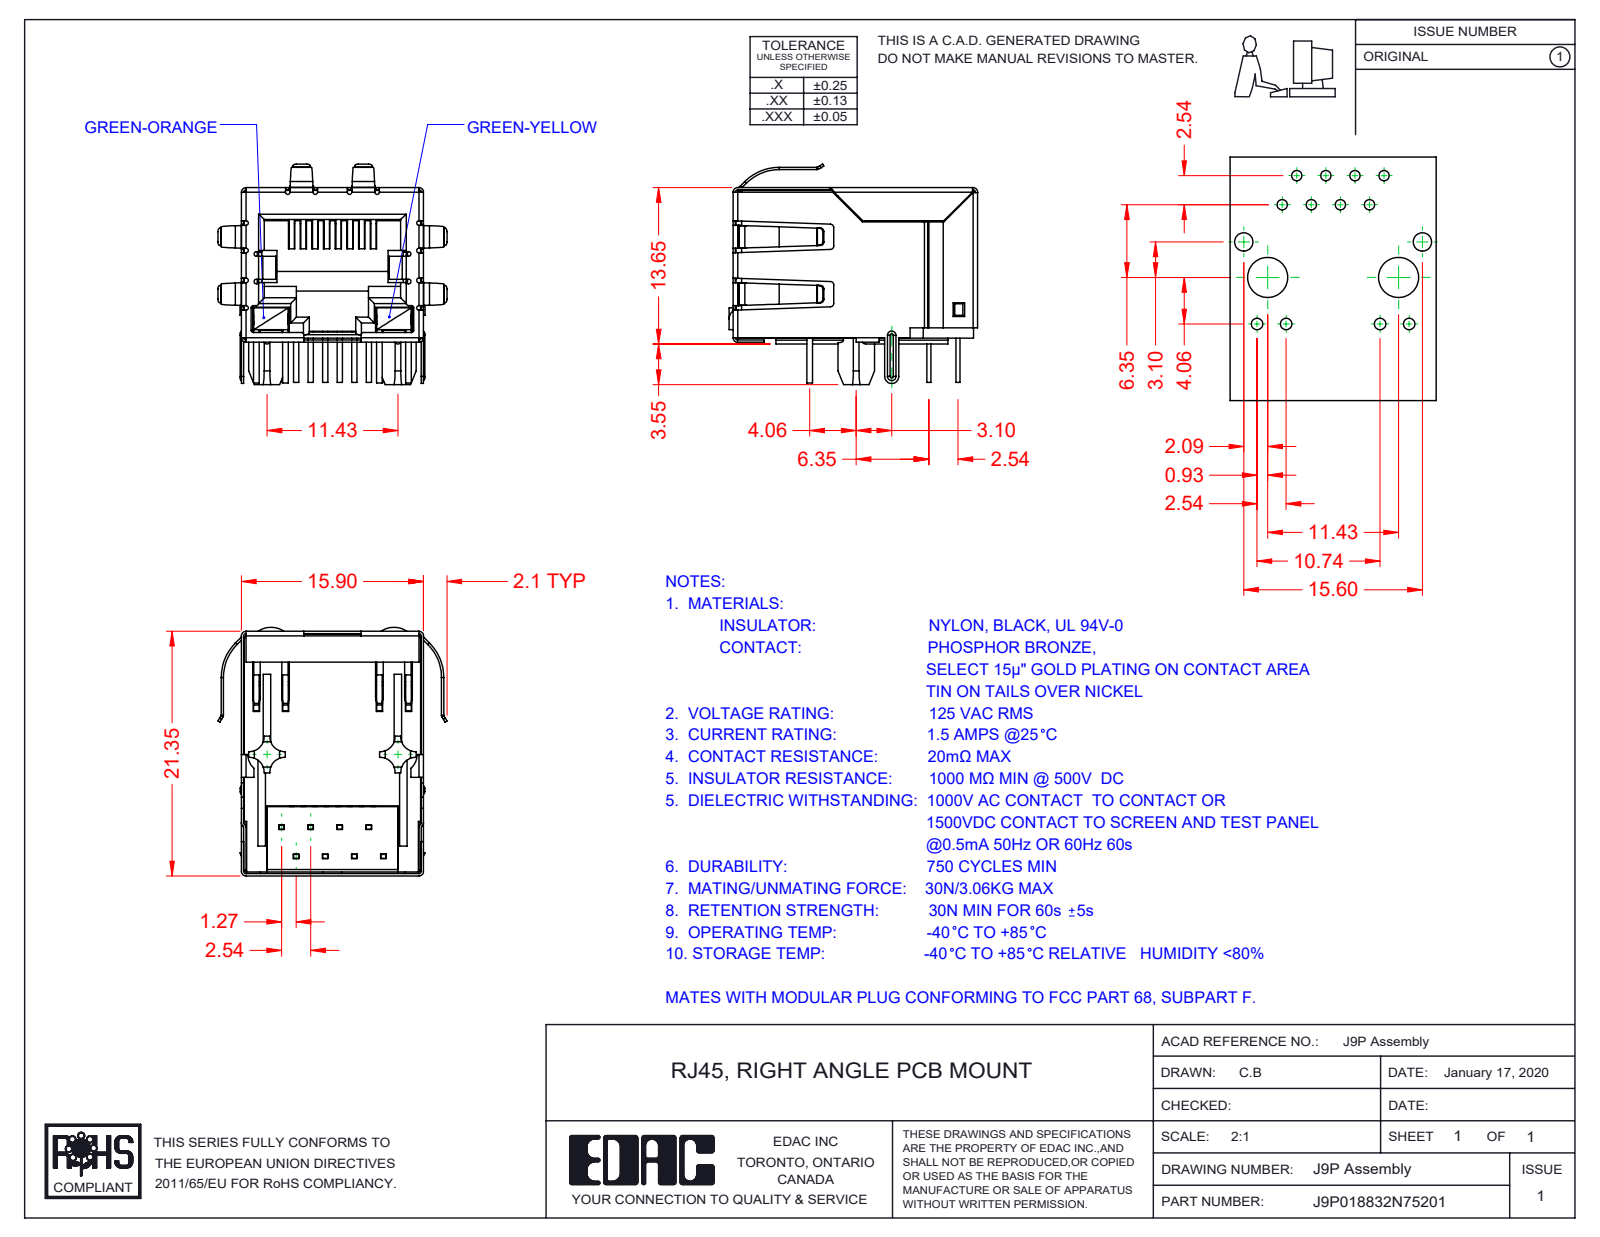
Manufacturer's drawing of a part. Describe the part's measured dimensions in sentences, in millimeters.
The part is named "9P-LED LED RH_5-Green-Yellow; J9P018832N75202; 9P-LED Assembly; 9P-LED Insulator (+4 more)". Its 3-D file was written by "SolidWorks 2016 (CONFIG_CONTROL_DESIGN)". It is 13 solids with 1476 faces: 1042 planar, 340 cylindrical and 94 other. Overall it measures 21.7 by 20 by 19.25 millimeters. Its volume is 2 687 cubic millimeters and its surface area 7 515 square millimeters. Partial cylindrical surfaces (rounded edges, fillets, slot ends): 39 of radius 0.2, 22 of radius 0.5, 20 of radius 0.3, 16 of radius 0.4, 8 of radius 1.3, 5 of radius 0.23, 4 of radius 0.11, 4 of radius 0.31. The main face-to-face distances are 15.45, 15.7, 15.65, 0.35, 0.54, 15.5, 12.36, 0.6, 1.4, 0.59.
